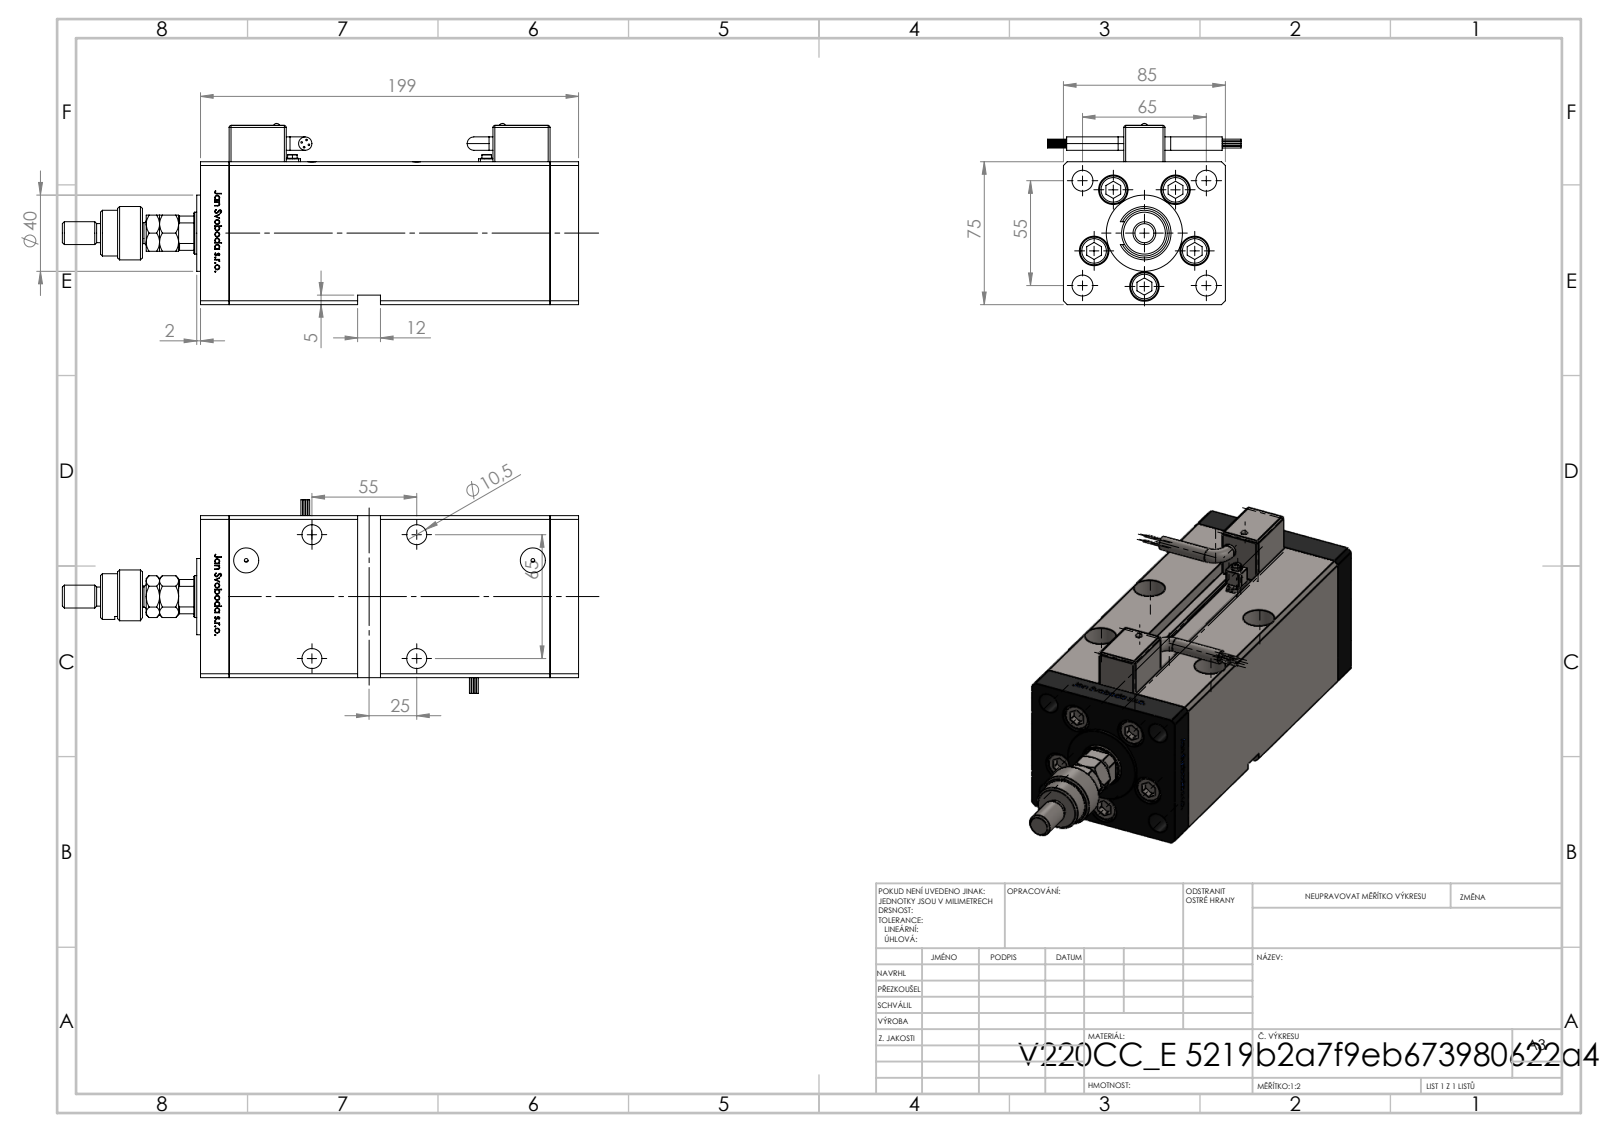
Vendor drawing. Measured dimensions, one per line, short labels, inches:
name: Magnetic_Switch_MSU4; V220C_FRONT_E; V220C_E MIDDLE; V220C_VC_E (+4 more)
written by: SolidWorks 2019 (CONFIG_CONTROL_DESIGN)
unit: in
bodies: 18 solids, 1503 faces (581 planar, 268 cylindrical, 654 other)
size: 10.669 × 4 × 3.744
volume: 69.08 in³; area: 312 in²
holes: 9× ⌀0.433, 5× ⌀0.61, 4× ⌀0.413, 4× ⌀0.65, 2× ⌀0.079, 2× ⌀0.142, 2× ⌀0.197, 2× ⌀0.276, 2× ⌀0.518, 1× ⌀0.531, 1× ⌀0.866, 1× ⌀0.925
bosses: 8× ⌀0.033, 5× ⌀0.571, 5× ⌀0.315, 4× ⌀0.276, 2× ⌀0.236, 2× ⌀0.138, 2× ⌀0.098, 1× ⌀1.575
rounds: 24× R0.039, 4× R0.157, 2× R0.037, 1× R0.384, 1× R0.413
face distances: 3.346, 2.953, 0.591, 6.634, 7.224, 7.815, 2.697, 1.348, 0.413, 0.256
hole spacings: 1.102, 1.676, 2.165, 2.559, 3.352, 0.325, 0.664, 0.755
